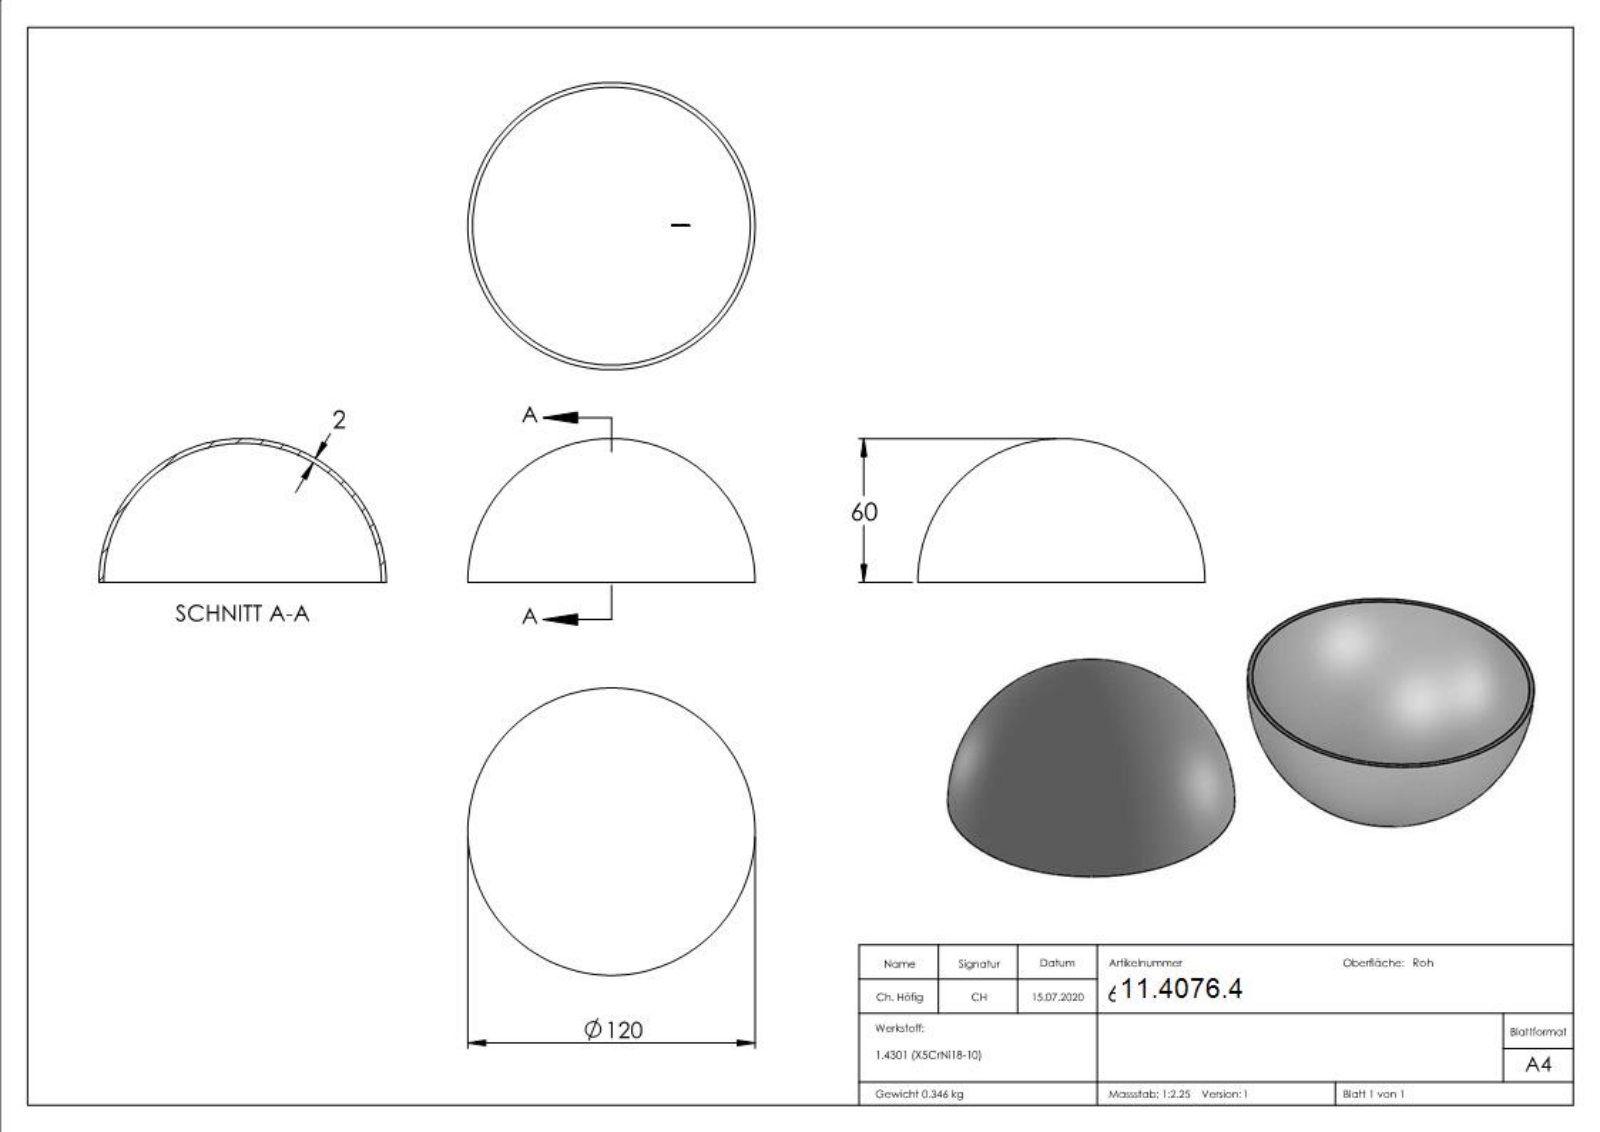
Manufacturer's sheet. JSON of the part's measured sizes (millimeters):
{"part_name": "620120-VA", "step_written_by": "SolidWorks 2018 (CONFIG_CONTROL_DESIGN)", "units": "millimeters", "bodies": {"solids": 1, "faces": 211, "planar": 98, "cylindrical": 0, "other": 113}, "overall_size": [120, 120, 60], "volume_mm3": 43748, "surface_area_mm2": 44502, "face_to_face_distances": [0.45, 5.1, 0.53, 3.79, 0.61, 1.19, 0.55, 0.85, 0.5, 0.81]}
